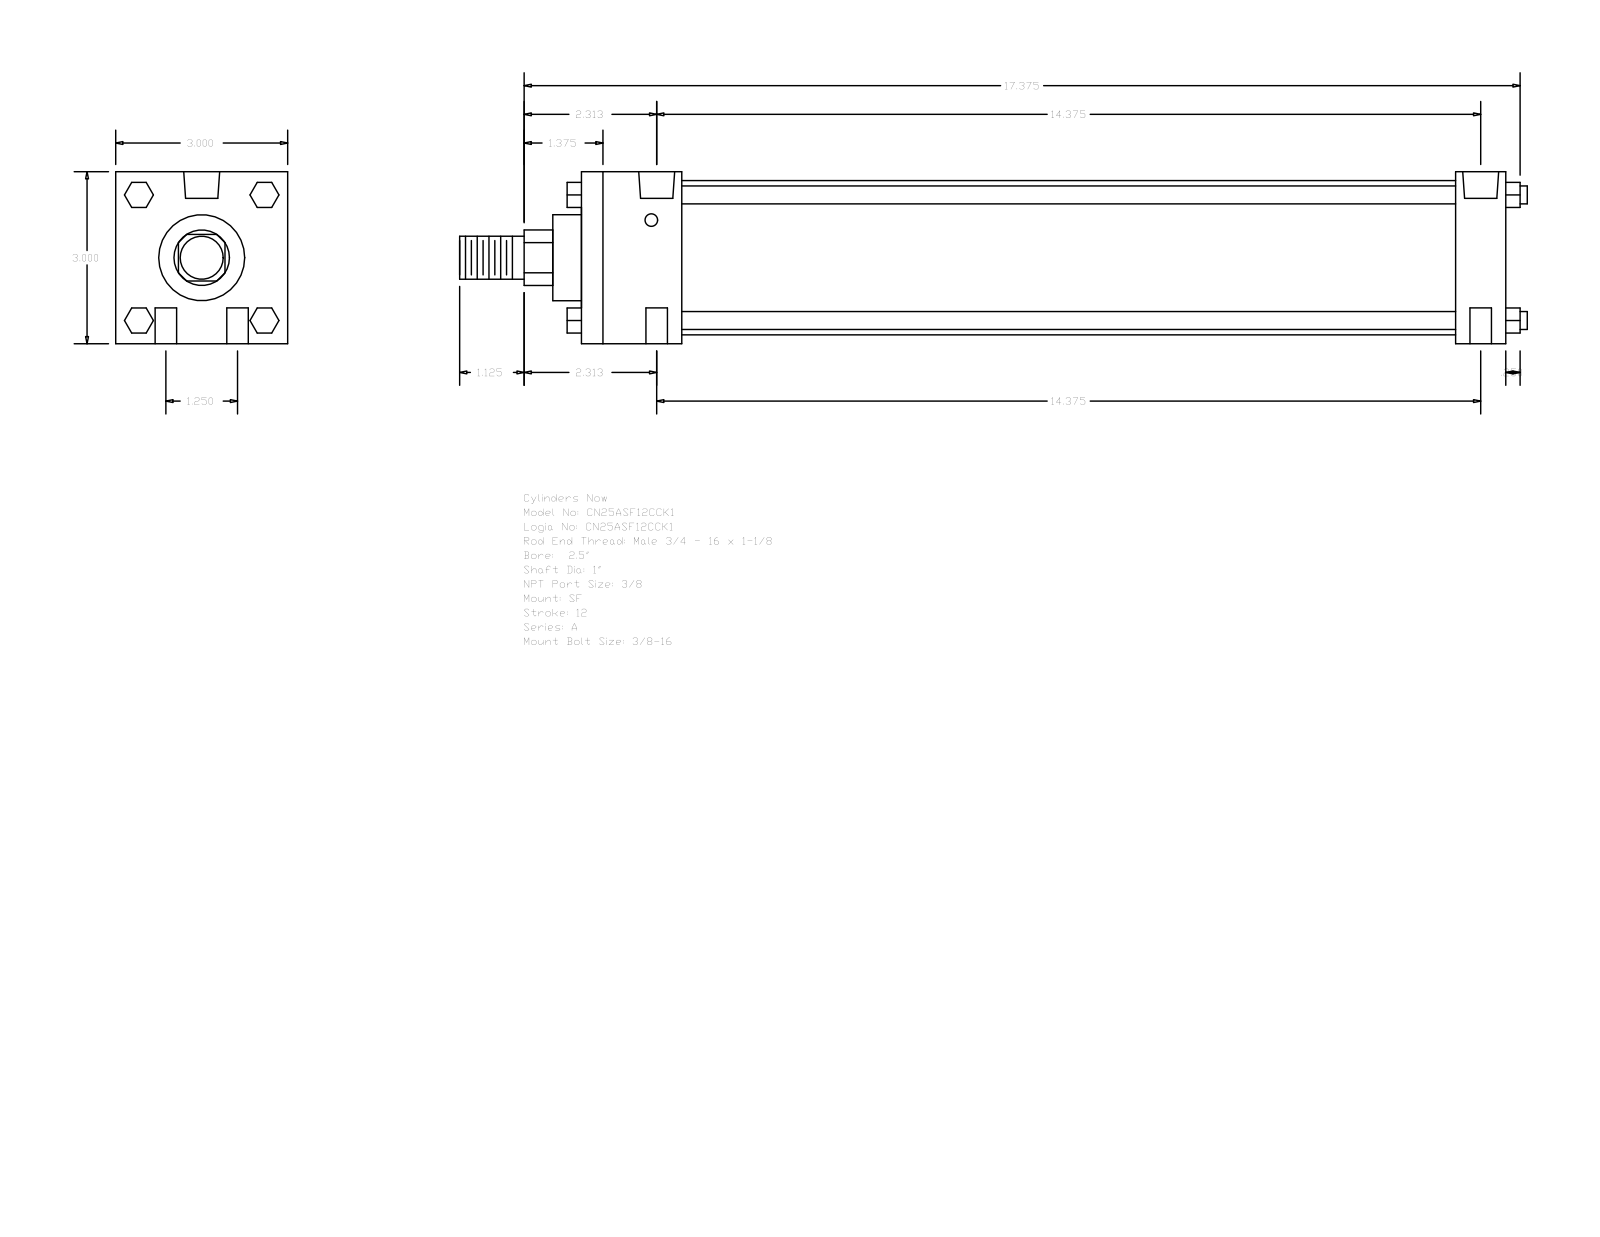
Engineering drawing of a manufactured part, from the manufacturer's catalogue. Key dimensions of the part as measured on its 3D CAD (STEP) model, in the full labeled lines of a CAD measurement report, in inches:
Part name (STEP PRODUCT): A_SF__0250_1
STEP written by: GSSL Pune (CONFIG_CONTROL_DESIGN)
Units: inches
Bodies: 0 solids, 124 faces (94 planar, 30 cylindrical, 0 other)
Overall size (bounding box): 18.625 × 3 × 3
Round holes (diameter × count): ⌀0.375 ×4, ⌀0.219 ×2, ⌀0.627 ×2
Round bosses / shafts (diameter × count): ⌀0.313 ×4, ⌀2.69 ×1, ⌀1.5 ×1, ⌀1 ×1, ⌀0.75 ×1
Partial cylindrical surfaces — rounded edges, fillets, slot ends (radius × count): R0.484 ×1
Main face-to-face distances: 3, 16.125, 15.25, 0.875, 1.75, 13.5, 14.375, 0.5, 0.437, 2.25
Hole centre spacings: 0.625, 14.389, 14.375, 1.25, 14.429, 14.562
